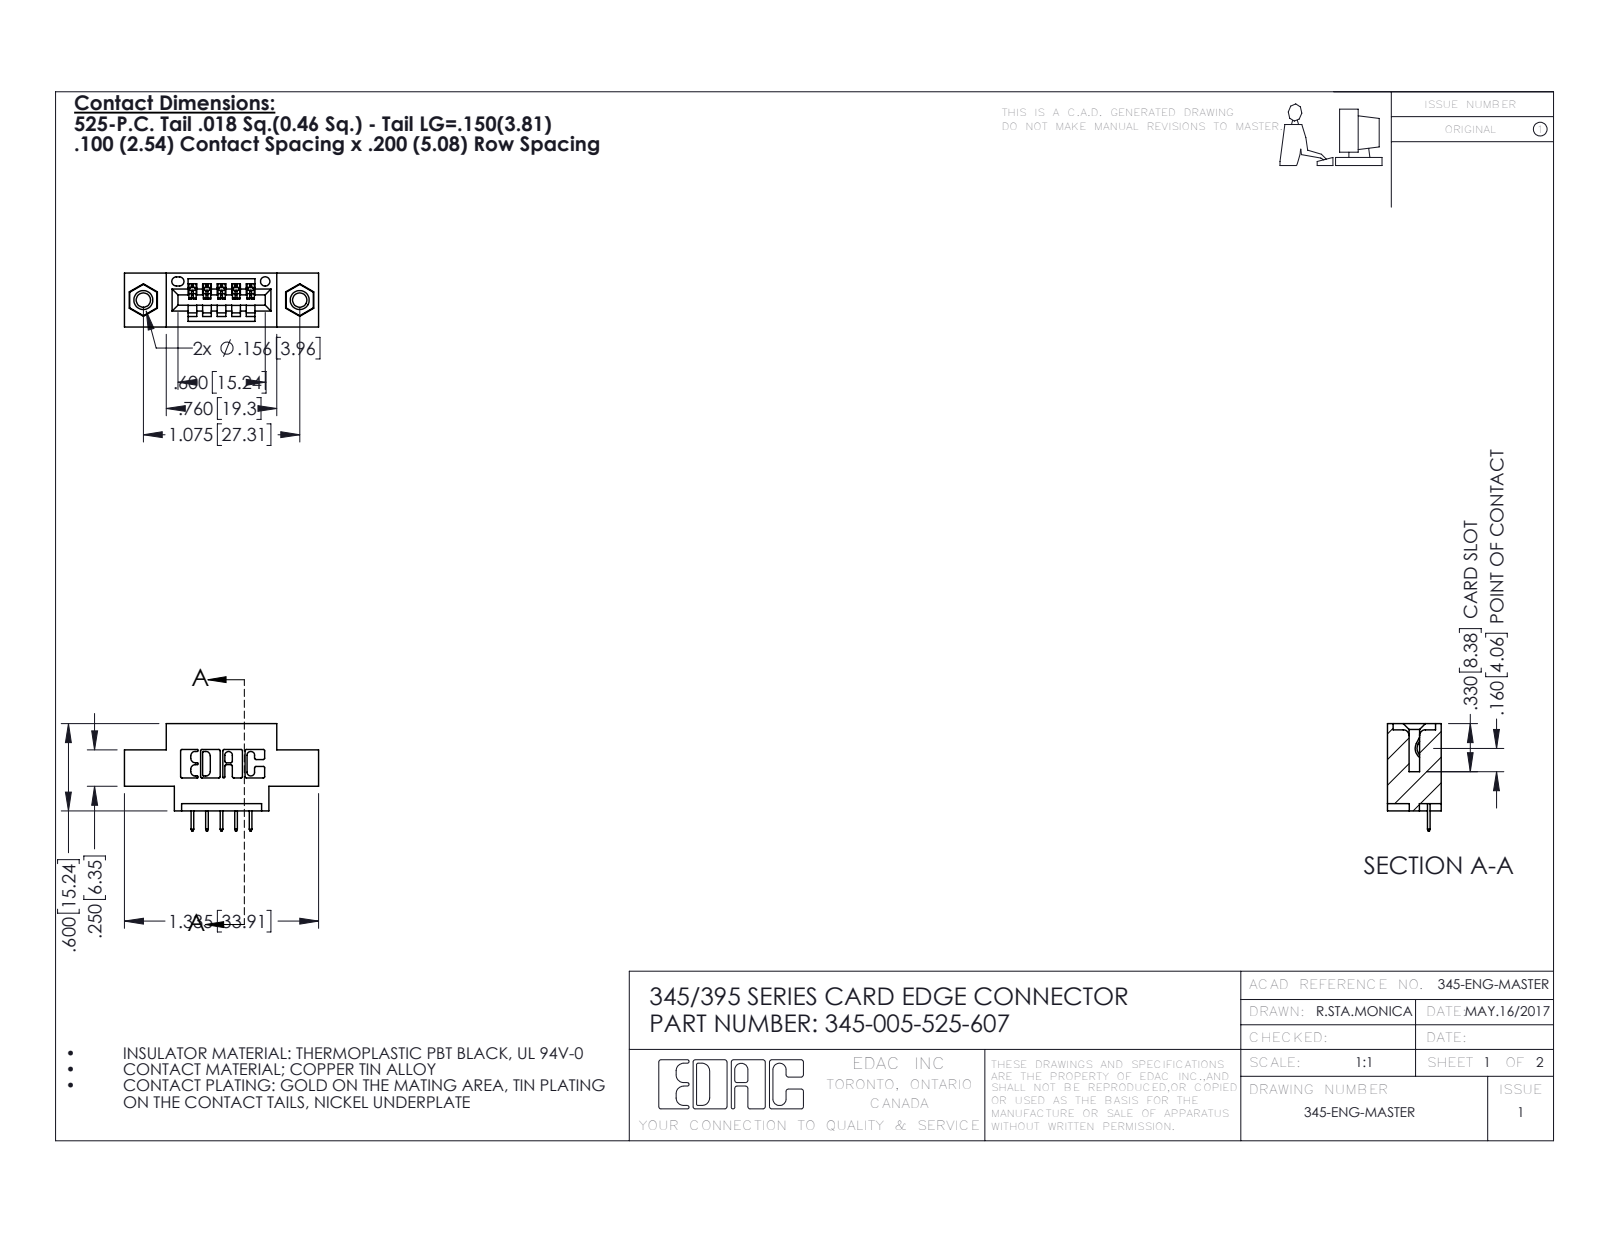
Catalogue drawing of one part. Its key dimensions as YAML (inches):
part_name: "345-292-001_345-293-125; 345-005-525-607; 345 Part_0.170 Offset - 0.156 Dia-TI; 345-250-001_345-250-005-103"
step_written_by: "SolidWorks 2020 (CONFIG_CONTROL_DESIGN)"
units: inches
bodies: {solids: 8, faces: 500, planar: 346, cylindrical: 138, other: 16}
overall_size: [1.335, 0.737, 0.37]
volume: 0.169
surface_area: 5.068
round_holes:
  - {diameter: 0.098, count: 2}
  - {diameter: 0.125, count: 2}
  - {diameter: 0.156, count: 2}
  - {diameter: 0.064, count: 1}
round_bosses_or_shafts:
  - {diameter: 0.155, count: 2}
partial_cylinders:
  - {radius: 0.01, count: 22}
  - {radius: 0.006, count: 10}
  - {radius: 0.007, count: 6}
  - {radius: 0.031, count: 6}
  - {radius: 0.026, count: 3}
  - {radius: 0.031, count: 2}
  - {radius: 0.04, count: 2}
  - {radius: 0.014, count: 1}
face_to_face_distances: [0.37, 0.2, 0.1, 0.072, 0.298, 0.025, 0.25, 0.06, 0.55, 0.15]
hole_center_spacings: [0.27, 0.847, 1.075]
